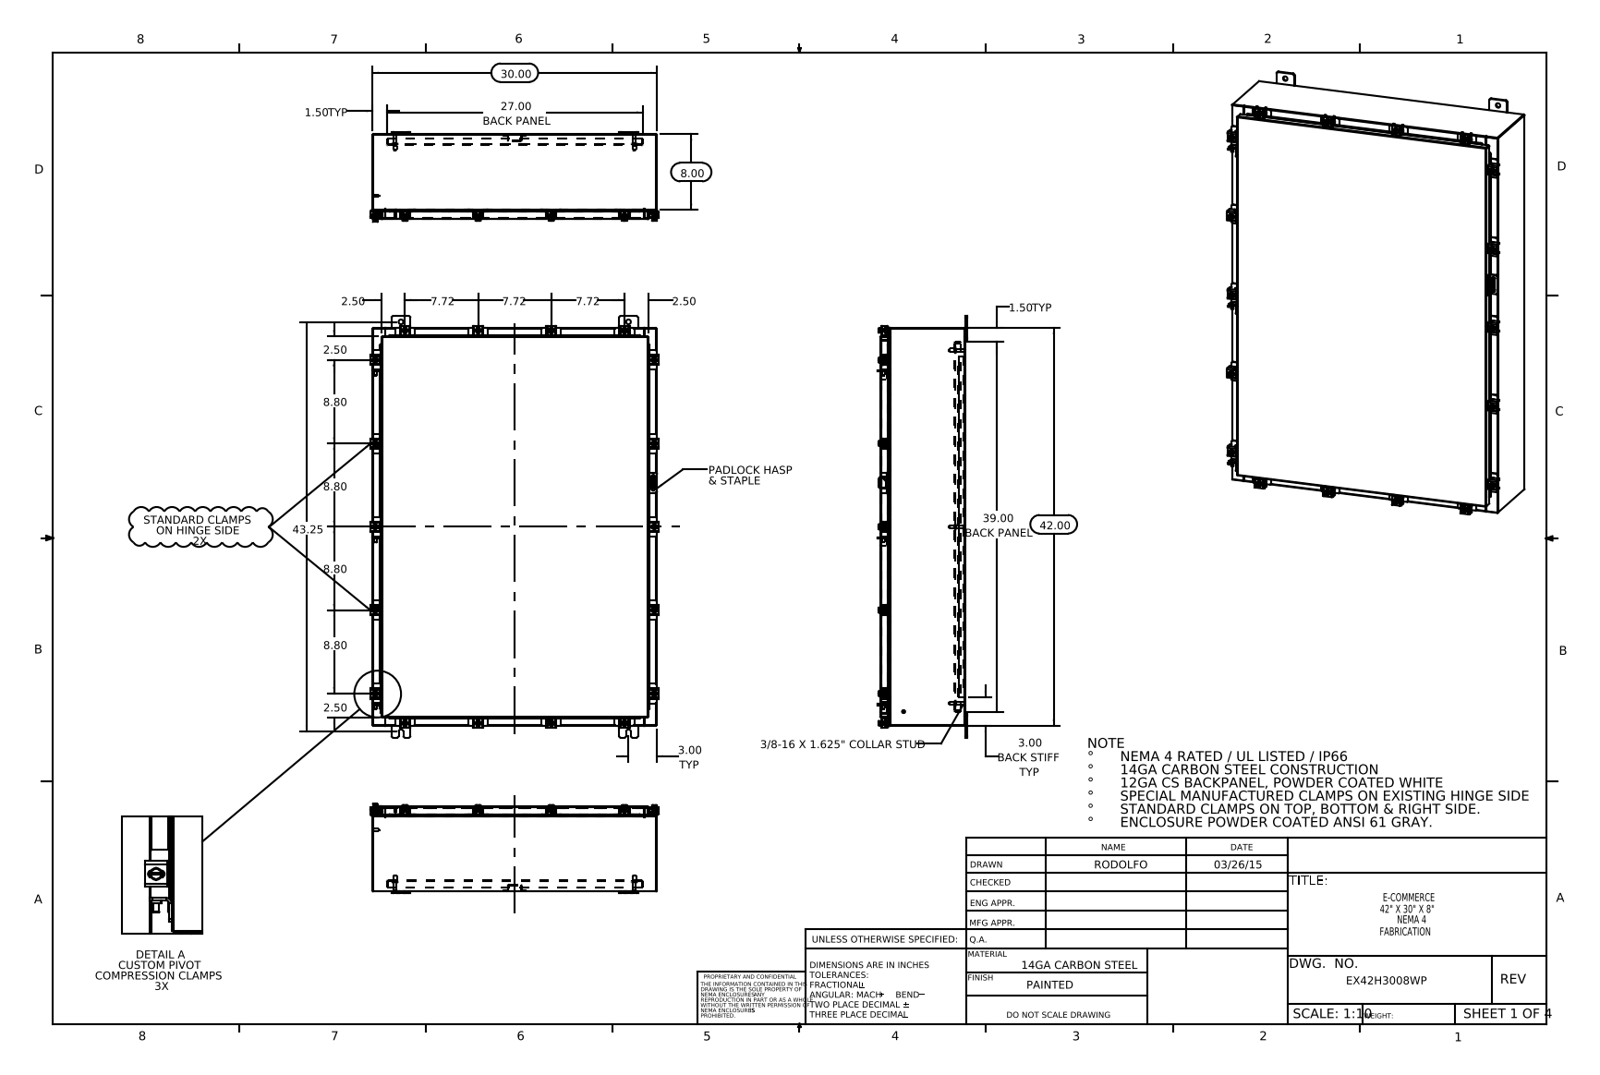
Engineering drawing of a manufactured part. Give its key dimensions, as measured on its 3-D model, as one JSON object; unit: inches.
{"part_name": "EX42H3008WP Body; HW-CLN-NH-20330; Special Clamp Assembly; EX42H3008WP Bottom (+8 more)", "step_written_by": "SolidWorks 2014 (CONFIG_CONTROL_DESIGN)", "units": "inches", "bodies": {"solids": 116, "faces": 2878, "planar": 1525, "cylindrical": 1123, "other": 230}, "overall_size": [44.5, 30.421, 9.453], "volume_in3": 437.9, "surface_area_in2": 10823, "round_holes": [[0.213, 18], [0.26, 18], [0.5, 10], [0.125, 1], [0.25, 1]], "round_bosses_or_shafts": [[0.5, 18], [0.25, 18], [0.399, 15], [0.625, 6], [0.375, 6], [0.33, 6], [0.315, 2], [0.236, 2]], "partial_cylinders_radius": [[0.06, 76], [0.141, 36], [0.12, 33], [0.013, 30], [0.09, 27], [0.088, 26], [0.05, 25], [0.145, 24]], "face_to_face_distances": [0.075, 8.9, 8.826, 8.975, 0.104, 1, 1.075, 7.826, 7.9, 1.179], "hole_center_spacings": [30.737, 29.451, 2.347, 4.44, 8.798, 17.719, 18.625, 20.752]}
